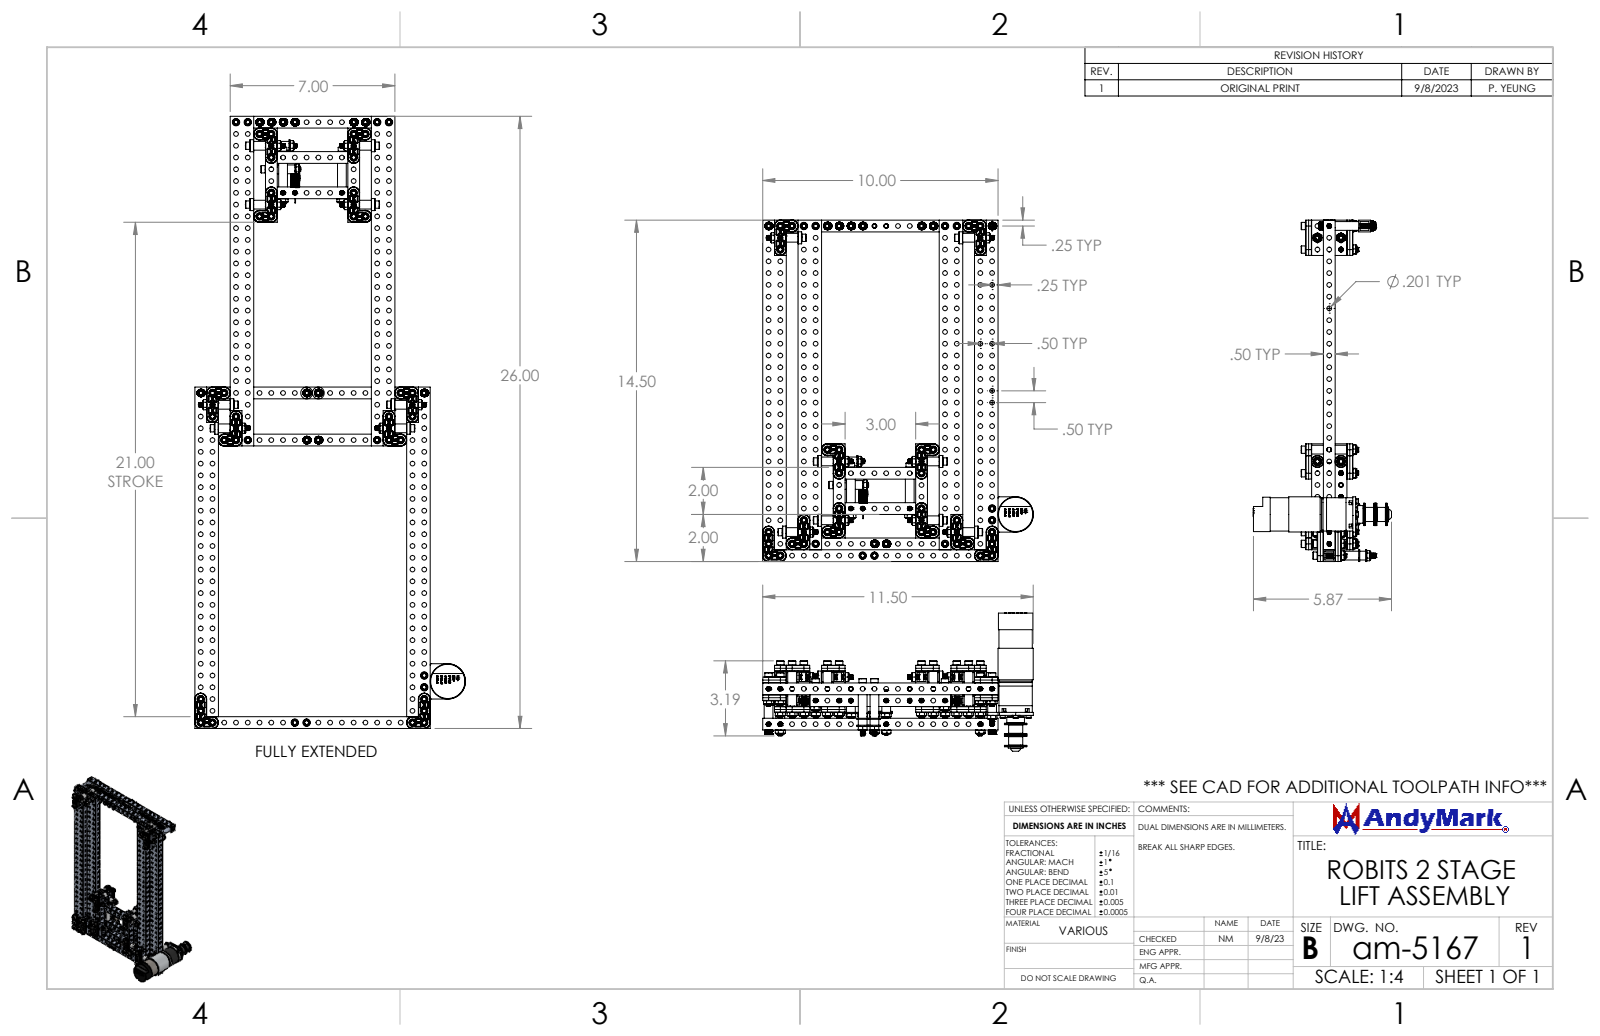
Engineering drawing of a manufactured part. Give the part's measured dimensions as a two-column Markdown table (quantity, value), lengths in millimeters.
| quantity | value |
| --- | --- |
| part name | NeveRest Orbital with 375H Adapter_13.7; am-4724 5 mm ID 13 mm OD Shielded Bearing_am-4724 5mm ID 13mm OD Shielded Radial Bearing; Elevator Corner Bearing Assembly_Through Bolt; am-1048 10-32 x 1750 SHCS_am-1048 10-32 x 1750 SHCS (+8 more) |
| STEP written by | SolidWorks 2024 (AUTOMOTIVE_DESIGN) |
| units | millimeters |
| bodies | 1003 solids, 34408 faces (5869 planar, 13474 cylindrical, 15065 other) |
| overall size | 368.5 × 292.1 × 149.2 |
| volume | 564 900 mm³ |
| surface area | 631 700 mm² |
| round holes (diameter × count) | 5.1 × 404, 4.2 × 280, 4.1 × 62, 6.1 × 62, 4.9 × 36, 5 × 16, 8.2 × 16, 9.8 × 16, 3.2 × 13, 2.5 × 10, 3.2 × 9, 5.6 × 9 |
| round bosses / shafts (diameter × count) | 4.8 × 65, 7.9 × 52, 9.5 × 36, 13 × 16, 8 × 12, 12.7 × 9, 5.5 × 8, 3 × 8 |
| partial cylindrical surfaces (radius × count) | 0.3 × 764, 2.1 × 70, 1.6 × 34, 1.6 × 22, 4.1 × 20, 0.7 × 4, 1.2 × 4, 1.5 × 4 |
| main face-to-face distances | 1.6, 12.7, 11.1, 25.4, 38.1, 23.8, 14.3, 9.5, 36.5, 190.5 |
| hole center spacings | 25.4, 12.7, 38.1, 63.5, 50.8, 76.2, 88.9, 101.6 |
